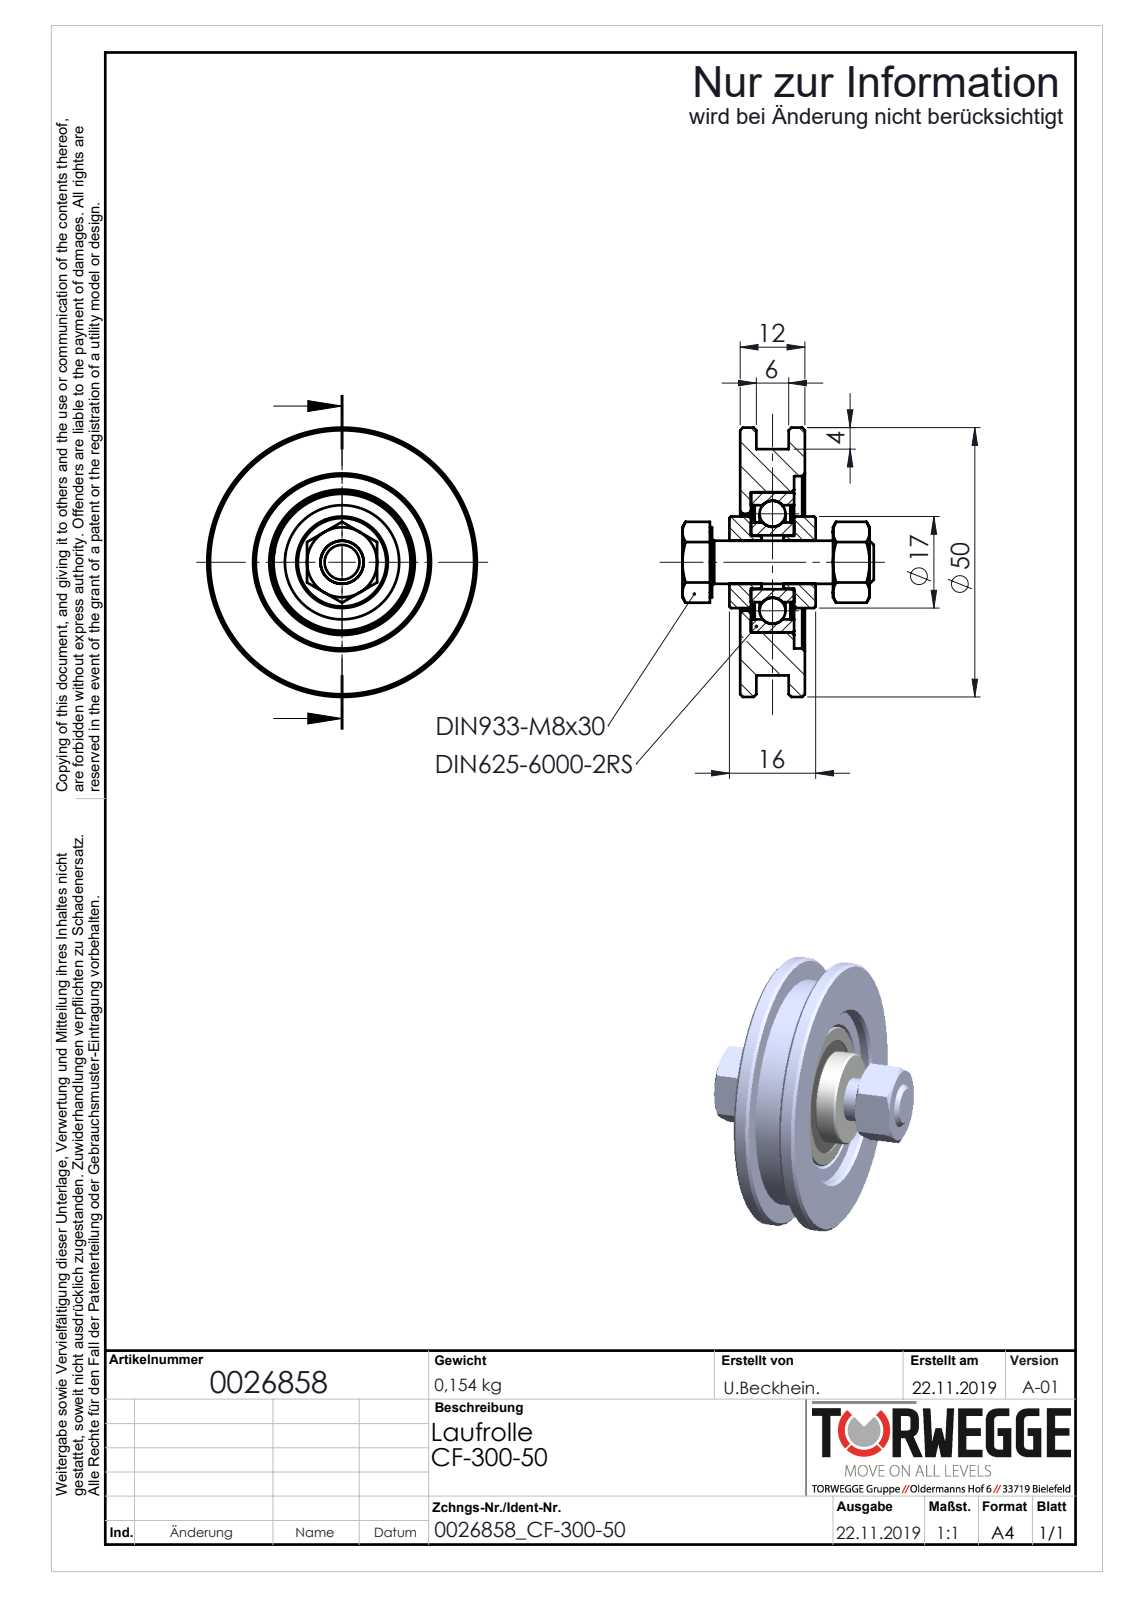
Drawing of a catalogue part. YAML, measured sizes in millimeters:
part_name: "0026858_CF-300-50_(A-01)"
step_written_by: "SolidWorks 2018 (AUTOMOTIVE_DESIGN)"
units: millimeters
bodies: {solids: 10, faces: 167, planar: 43, cylindrical: 52, other: 72}
overall_size: [50, 50, 35.5]
volume: 21276
surface_area: 14500
round_holes:
  - {diameter: 6.8, count: 1}
  - {diameter: 8, count: 1}
  - {diameter: 10, count: 1}
  - {diameter: 14.8, count: 1}
  - {diameter: 18, count: 1}
  - {diameter: 21.2, count: 1}
  - {diameter: 26, count: 1}
  - {diameter: 32, count: 1}
round_bosses_or_shafts:
  - {diameter: 50, count: 1}
  - {diameter: 42, count: 1}
  - {diameter: 17, count: 1}
  - {diameter: 13, count: 1}
  - {diameter: 9.8, count: 1}
face_to_face_distances: [2, 12, 10, 1, 3, 9, 7, 8, 6, 6.8]
